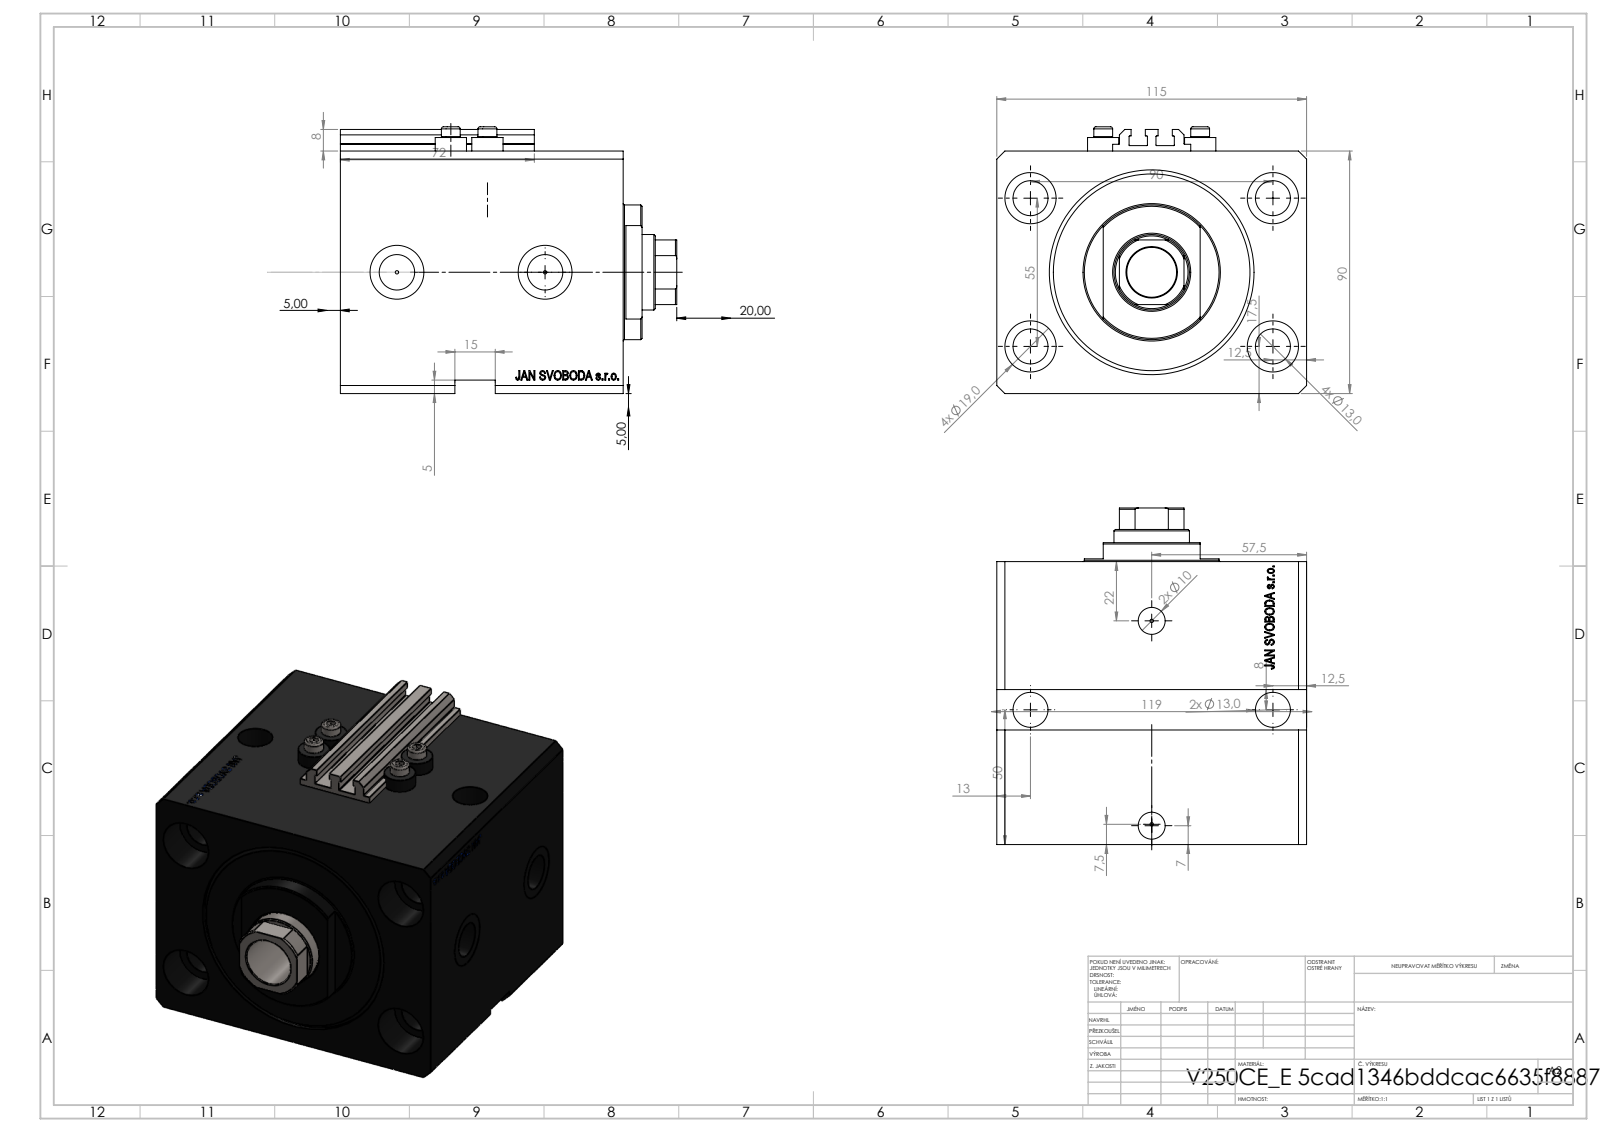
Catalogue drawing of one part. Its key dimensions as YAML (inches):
part_name: "V250CE_C_VCP; ALLEN BOLT V250CE; V250CE_VC_E; V250CE_E_Body"
step_written_by: "SolidWorks 2019 (CONFIG_CONTROL_DESIGN)"
units: inches
bodies: {solids: 8, faces: 1123, planar: 547, cylindrical: 138, other: 438}
overall_size: [4.917, 4.528, 3.898]
volume: 58.03
surface_area: 244.4
round_holes:
  - {diameter: 0.512, count: 6}
  - {diameter: 0.049, count: 4}
  - {diameter: 0.157, count: 4}
  - {diameter: 0.748, count: 4}
  - {diameter: 0.394, count: 2}
  - {diameter: 0.518, count: 2}
  - {diameter: 0.787, count: 2}
  - {diameter: 0.728, count: 1}
  - {diameter: 1.102, count: 1}
  - {diameter: 2.48, count: 1}
  - {diameter: 2.992, count: 1}
round_bosses_or_shafts:
  - {diameter: 0.457, count: 4}
  - {diameter: 0.276, count: 4}
  - {diameter: 1.969, count: 1}
partial_cylinders:
  - {radius: 0.008, count: 10}
  - {radius: 0.531, count: 1}
face_to_face_distances: [3.543, 4.528, 4.134, 3.429, 0.705, 2.244, 2.949, 1.185, 0.787, 2.161]
hole_center_spacings: [2.076, 2.165, 3.543, 0.535, 1.078, 1.12, 1.324, 1.417]
